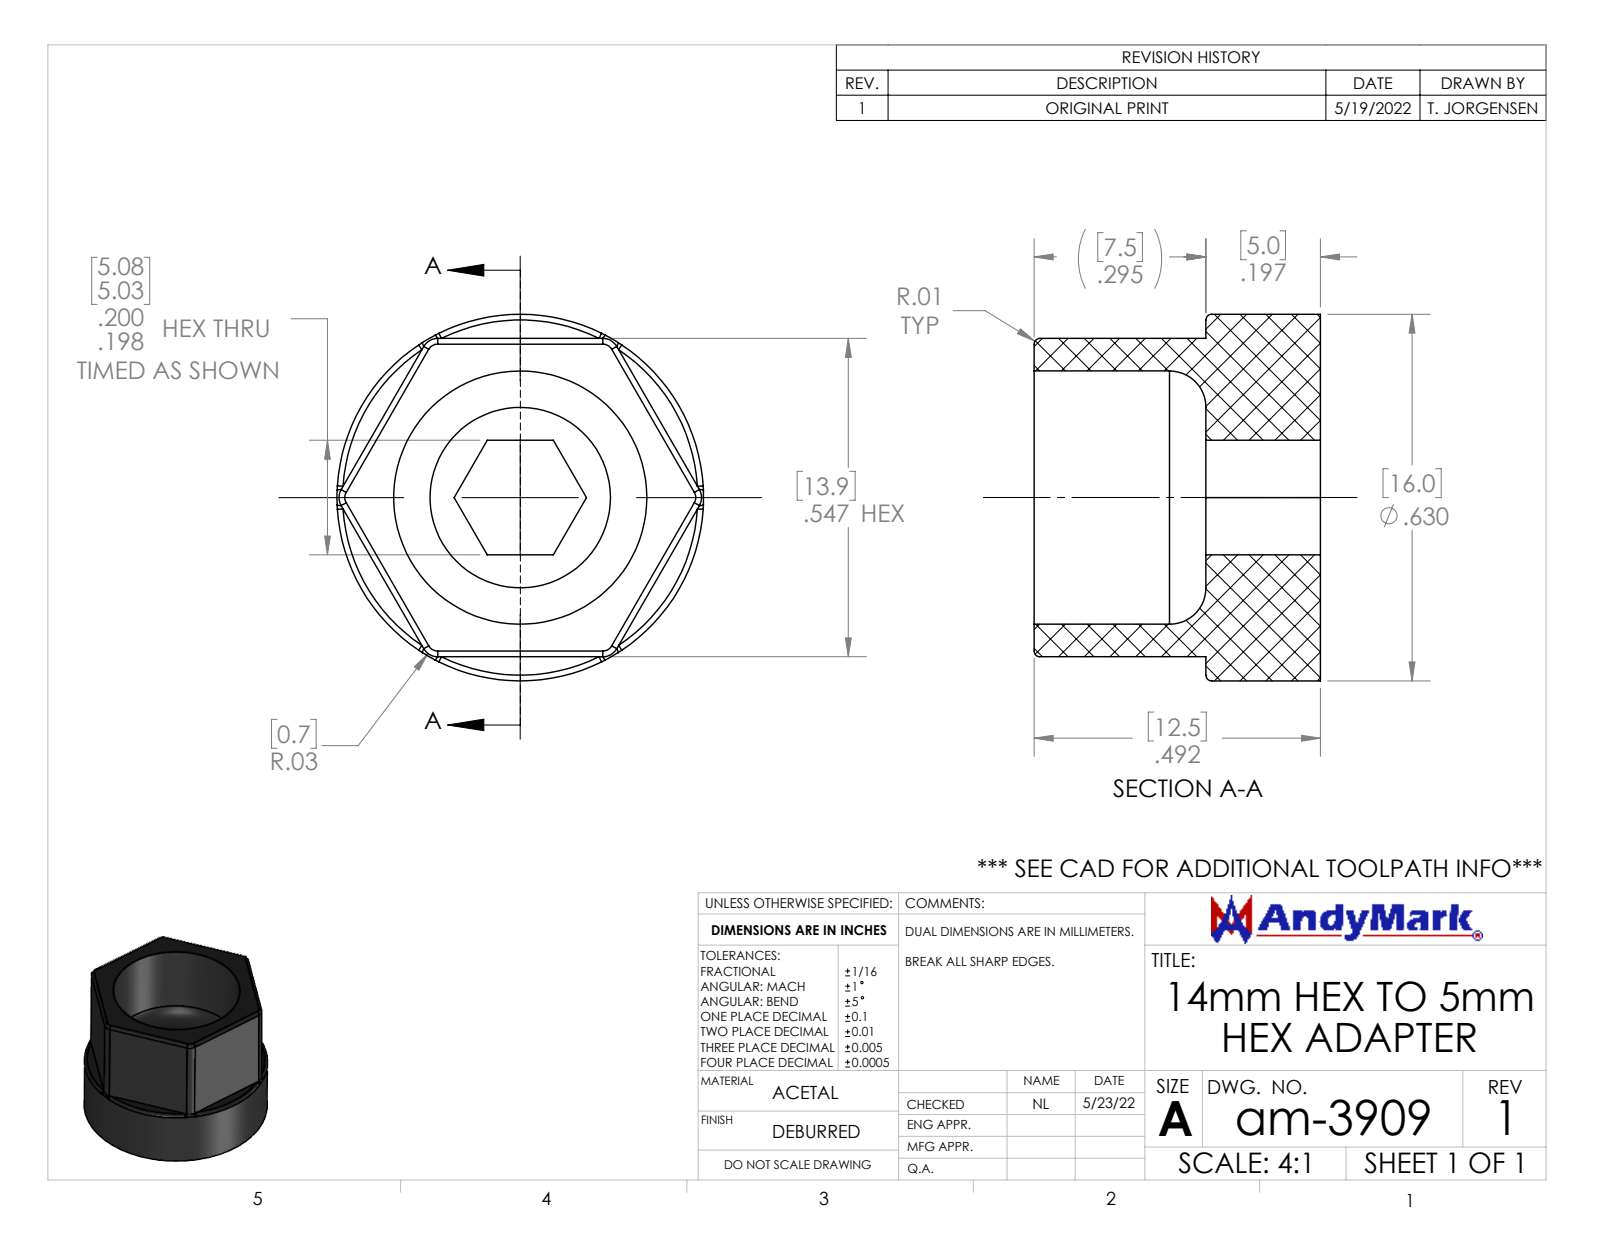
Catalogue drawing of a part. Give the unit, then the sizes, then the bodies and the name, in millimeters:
Units: millimetres
Overall size (bounding box): 16 × 16 × 12.5
Round holes (diameter × count): ⌀11 ×1
Round bosses / shafts (diameter × count): ⌀16 ×1
Partial cylindrical surfaces — rounded edges, fillets, slot ends (radius × count): R0.3 ×6, R0.7 ×6
Main face-to-face distances: 13.9, 5, 4.4, 9.4, 12.5, 13.9, 7.5, 9.4, 4.4
Volume: 1 400 mm³ · Surface area: 1 279 mm²
Bodies: 1 solid, 71 faces (21 planar, 17 cylindrical, 33 other)
Part name (STEP PRODUCT): am-3909 14mm Hex to 5mm Hex
STEP written by: SolidWorks 2021 (CONFIG_CONTROL_DESIGN)
